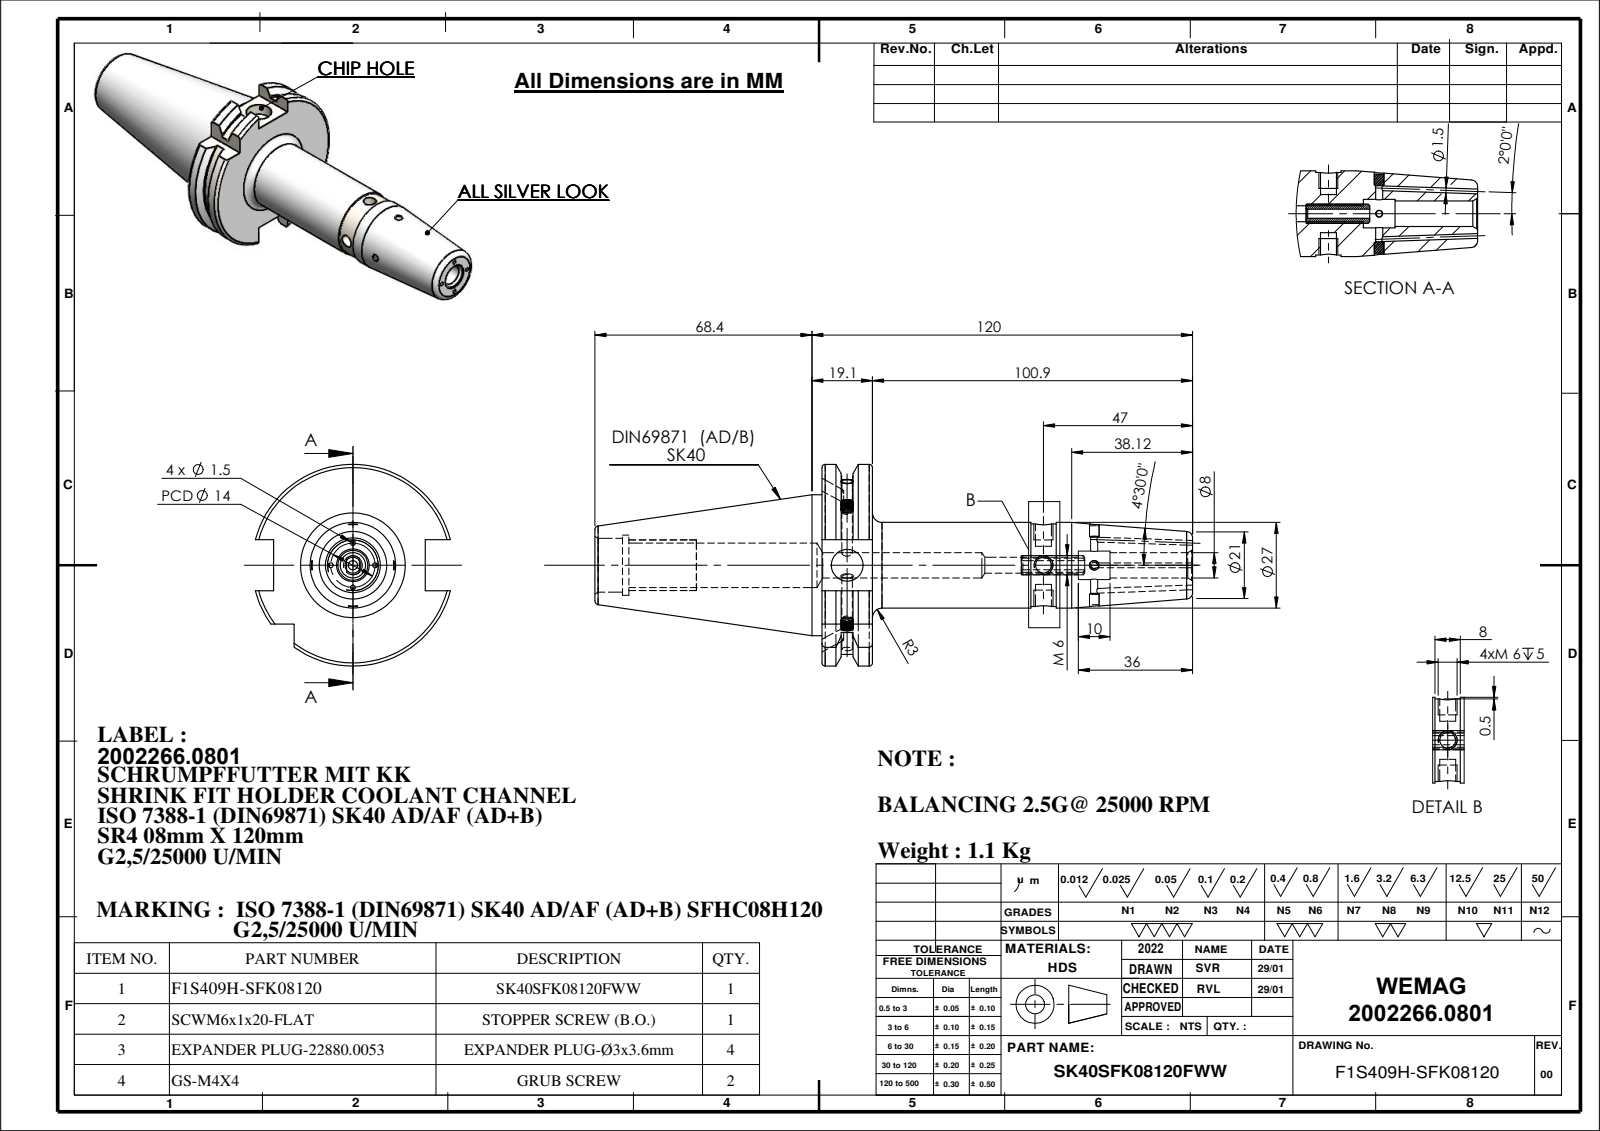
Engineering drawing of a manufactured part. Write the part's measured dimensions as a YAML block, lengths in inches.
part_name: "EXPANDER PLUG Ø3x3.6; GS-M4X4_DIN 913 - M4 x 4-N; SCWM6x1x20-FLAT; 91406-SR408120 (+1 more)"
step_written_by: "SolidWorks 2018 (CONFIG_CONTROL_DESIGN)"
units: inches
bodies: {solids: 8, faces: 291, planar: 66, cylindrical: 105, other: 120}
overall_size: [7.417, 2.502, 2.42]
volume: 9.049
surface_area: 52.02
round_holes:
  - {diameter: 0.059, count: 4}
  - {diameter: 0.197, count: 3}
  - {diameter: 0.087, count: 2}
  - {diameter: 0.118, count: 2}
  - {diameter: 0.114, count: 1}
  - {diameter: 0.13, count: 1}
  - {diameter: 0.315, count: 1}
  - {diameter: 0.315, count: 1}
  - {diameter: 0.354, count: 1}
  - {diameter: 0.394, count: 1}
  - {diameter: 0.551, count: 1}
  - {diameter: 0.669, count: 1}
round_bosses_or_shafts:
  - {diameter: 0.157, count: 2}
  - {diameter: 1.75, count: 1}
  - {diameter: 1.063, count: 1}
  - {diameter: 1.024, count: 1}
partial_cylinders:
  - {radius: 0.118, count: 1}
  - {radius: 1.107, count: 1}
  - {radius: 1.251, count: 1}
face_to_face_distances: [0.626, 0.634, 1.882, 4.598, 3.972, 0.157, 2.819, 3.445, 7.417, 0.421]
hole_center_spacings: [0.63, 2.435, 3.065]
